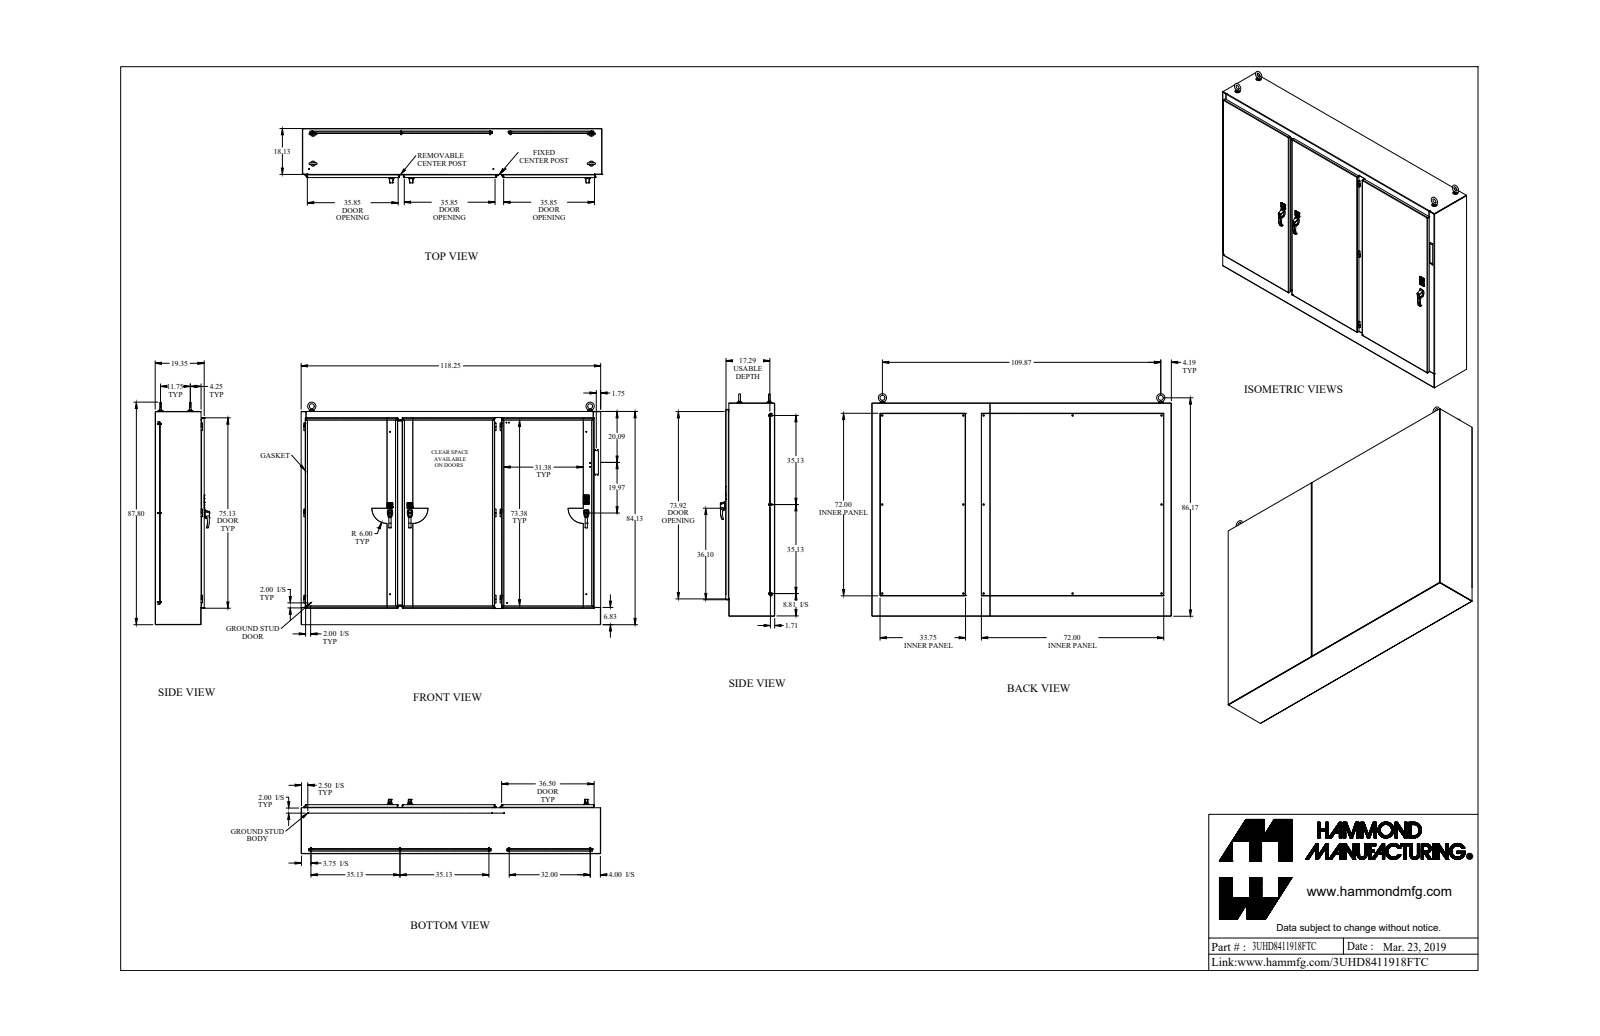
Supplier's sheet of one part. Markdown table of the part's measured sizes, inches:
| quantity | value |
| --- | --- |
| part name | 3UHD8411918FTC |
| STEP written by | SolidWorks 2018 (AUTOMOTIVE_DESIGN) |
| units | inches |
| bodies | 312 solids, 4330 faces (2618 planar, 1215 cylindrical, 497 other) |
| overall size | 118.25 × 87.799 × 21.464 |
| volume | 11 440 in³ |
| surface area | 84 520 in² |
| round holes (diameter × count) | 0.25 × 20, 0.196 × 19, 0.307 × 17, 0.281 × 12, 0.313 × 9, 0.35 × 9, 0.445 × 9, 0.875 × 8, 0.266 × 6, 0.39 × 6, 0.445 × 5, 0.257 × 4 |
| round bosses / shafts (diameter × count) | 1 × 20, 0.25 × 18, 0.375 × 15, 0.65 × 14, 0.33 × 14, 0.281 × 12, 0.246 × 10, 0.486 × 7 |
| partial cylindrical surfaces (radius × count) | 0.06 × 73, 0.125 × 62, 0.185 × 52, 0.017 × 48, 0.5 × 41, 0.03 × 18, 0.09 × 18, 0.13 × 16 |
| main face-to-face distances | 0.125, 0.072, 19.369, 19.243, 19.297, 19.172, 1.937, 1.812, 17.36, 17.431 |
| hole center spacings | 70.25, 35.125, 35.125, 2.126, 7.87, 11.75, 69.629, 77.499 |
